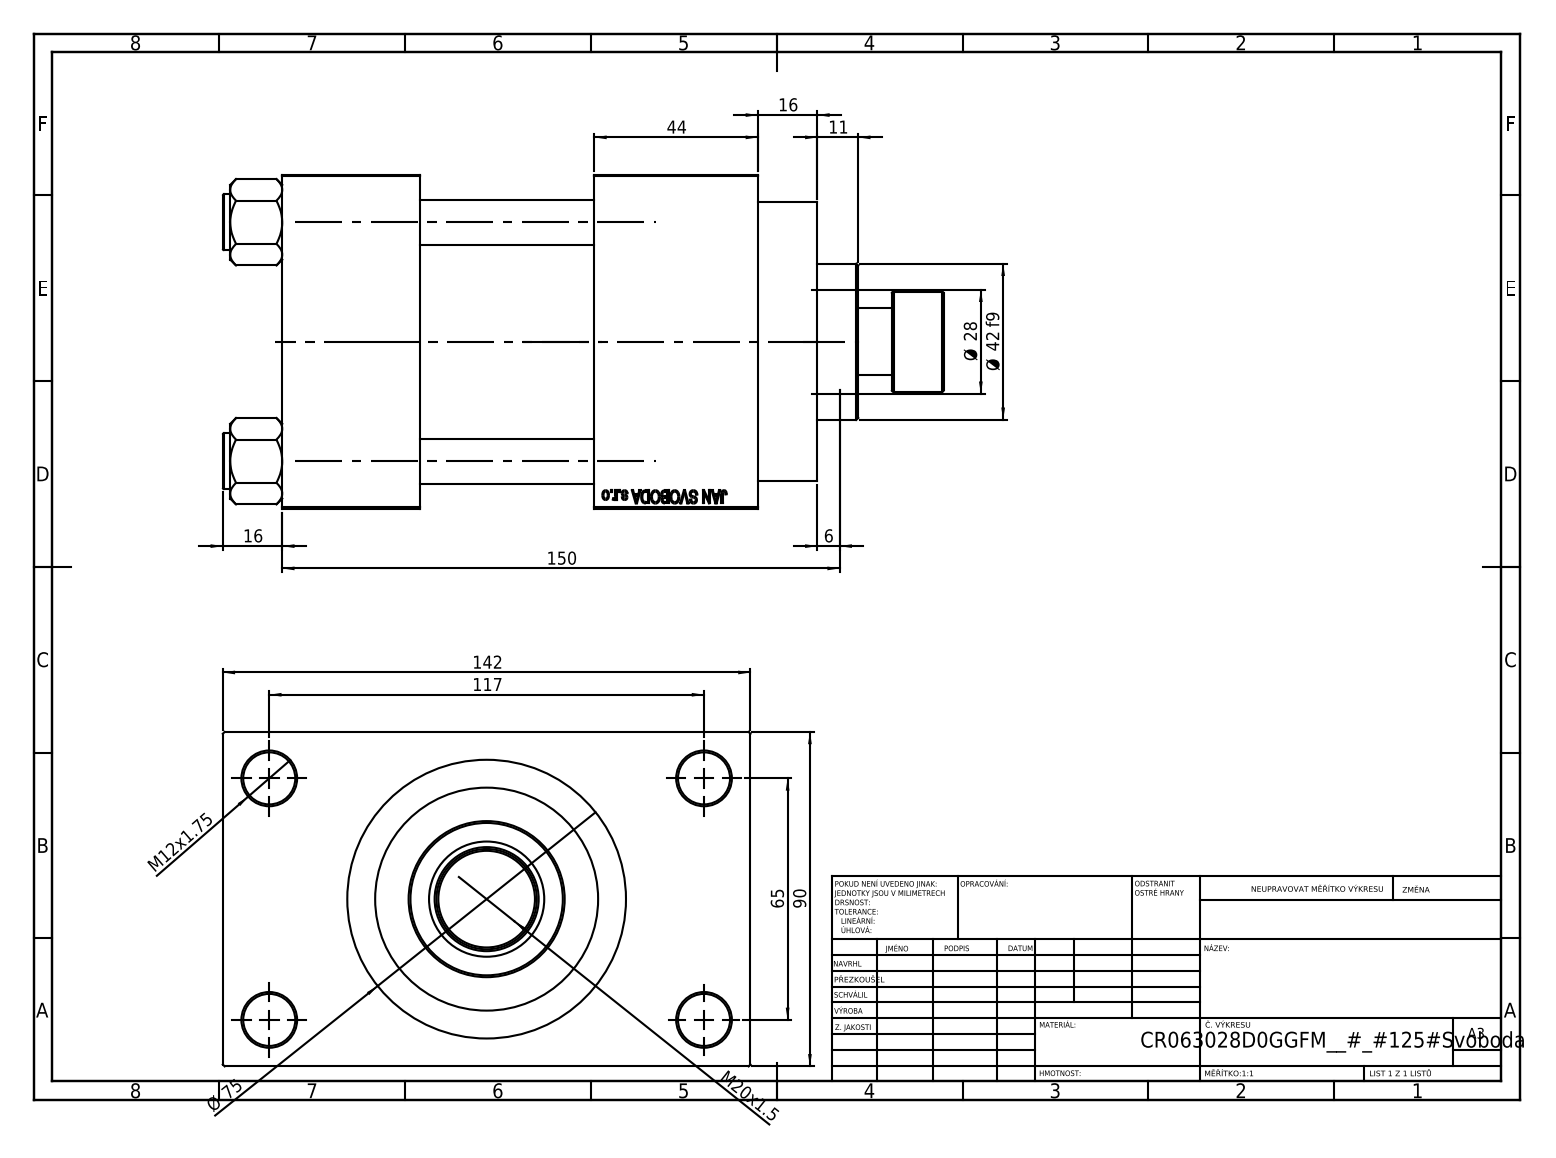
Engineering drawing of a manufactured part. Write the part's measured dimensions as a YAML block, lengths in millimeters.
part_name: "V215CR_VCP_D; V215CR_D_TYCINKA; V215_VC_A; NUT_M5_D (+2 more)"
step_written_by: "SolidWorks 2019 (CONFIG_CONTROL_DESIGN)"
units: millimeters
bodies: {solids: 12, faces: 1118, planar: 501, cylindrical: 93, other: 524}
overall_size: [194, 142, 90]
volume: 1042000
surface_area: 187940
round_holes:
  - {diameter: 12, count: 4}
  - {diameter: 14, count: 4}
  - {diameter: 7, count: 2}
  - {diameter: 20.96, count: 2}
  - {diameter: 30, count: 2}
  - {diameter: 18.5, count: 1}
  - {diameter: 28, count: 1}
  - {diameter: 31, count: 1}
  - {diameter: 50, count: 1}
  - {diameter: 60, count: 1}
  - {diameter: 63, count: 1}
round_bosses_or_shafts:
  - {diameter: 15, count: 4}
  - {diameter: 75, count: 1}
  - {diameter: 69, count: 1}
  - {diameter: 42, count: 1}
  - {diameter: 27, count: 1}
  - {diameter: 18, count: 1}
face_to_face_distances: [90, 47, 37, 84, 91, 128, 44, 26, 116, 64]
hole_center_spacings: [26.35, 45.47, 64.3, 66.92, 69.81, 90.65, 111.34, 65]
